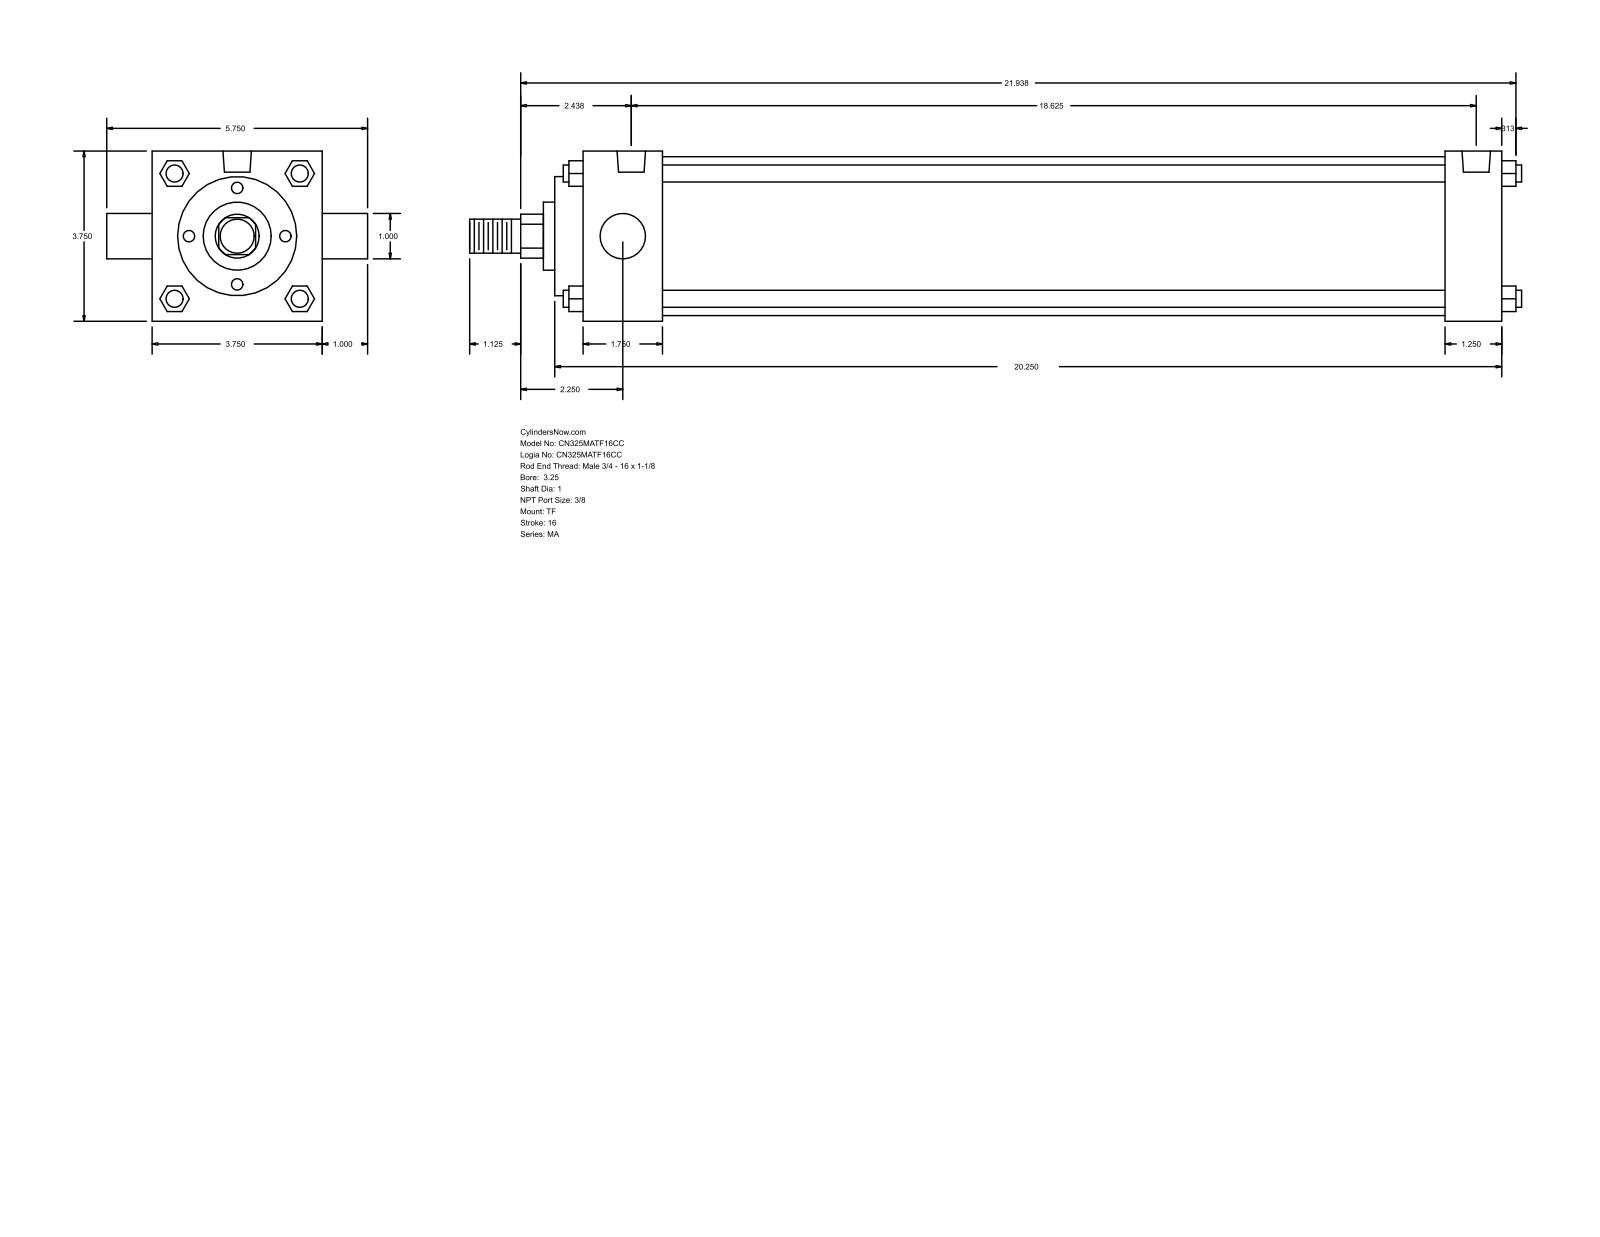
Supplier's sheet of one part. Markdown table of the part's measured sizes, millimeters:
| quantity | value |
| --- | --- |
| part name | MA_TF__0325_1 |
| STEP written by | GSSL Pune (CONFIG_CONTROL_DESIGN) |
| units | millimeters |
| bodies | 0 solids, 122 faces (93 planar, 29 cylindrical, 0 other) |
| overall size | 588.96 × 146.05 × 95.25 |
| round holes (diameter × count) | 11.11 × 3, 15.93 × 2 |
| round bosses / shafts (diameter × count) | 9.53 × 4, 25.4 × 2, 88.9 × 1, 66.67 × 1, 38.1 × 1, 19.05 × 1 |
| partial cylindrical surfaces (radius × count) | 12.29 × 1 |
| main face-to-face distances | 95.24, 514.35, 530.22, 44.46, 482.6, 438.14, 469.89, 31.75, 15.87, 60.33 |
| hole center spacings | 4.76, 468.32, 463.56, 473.08 |
